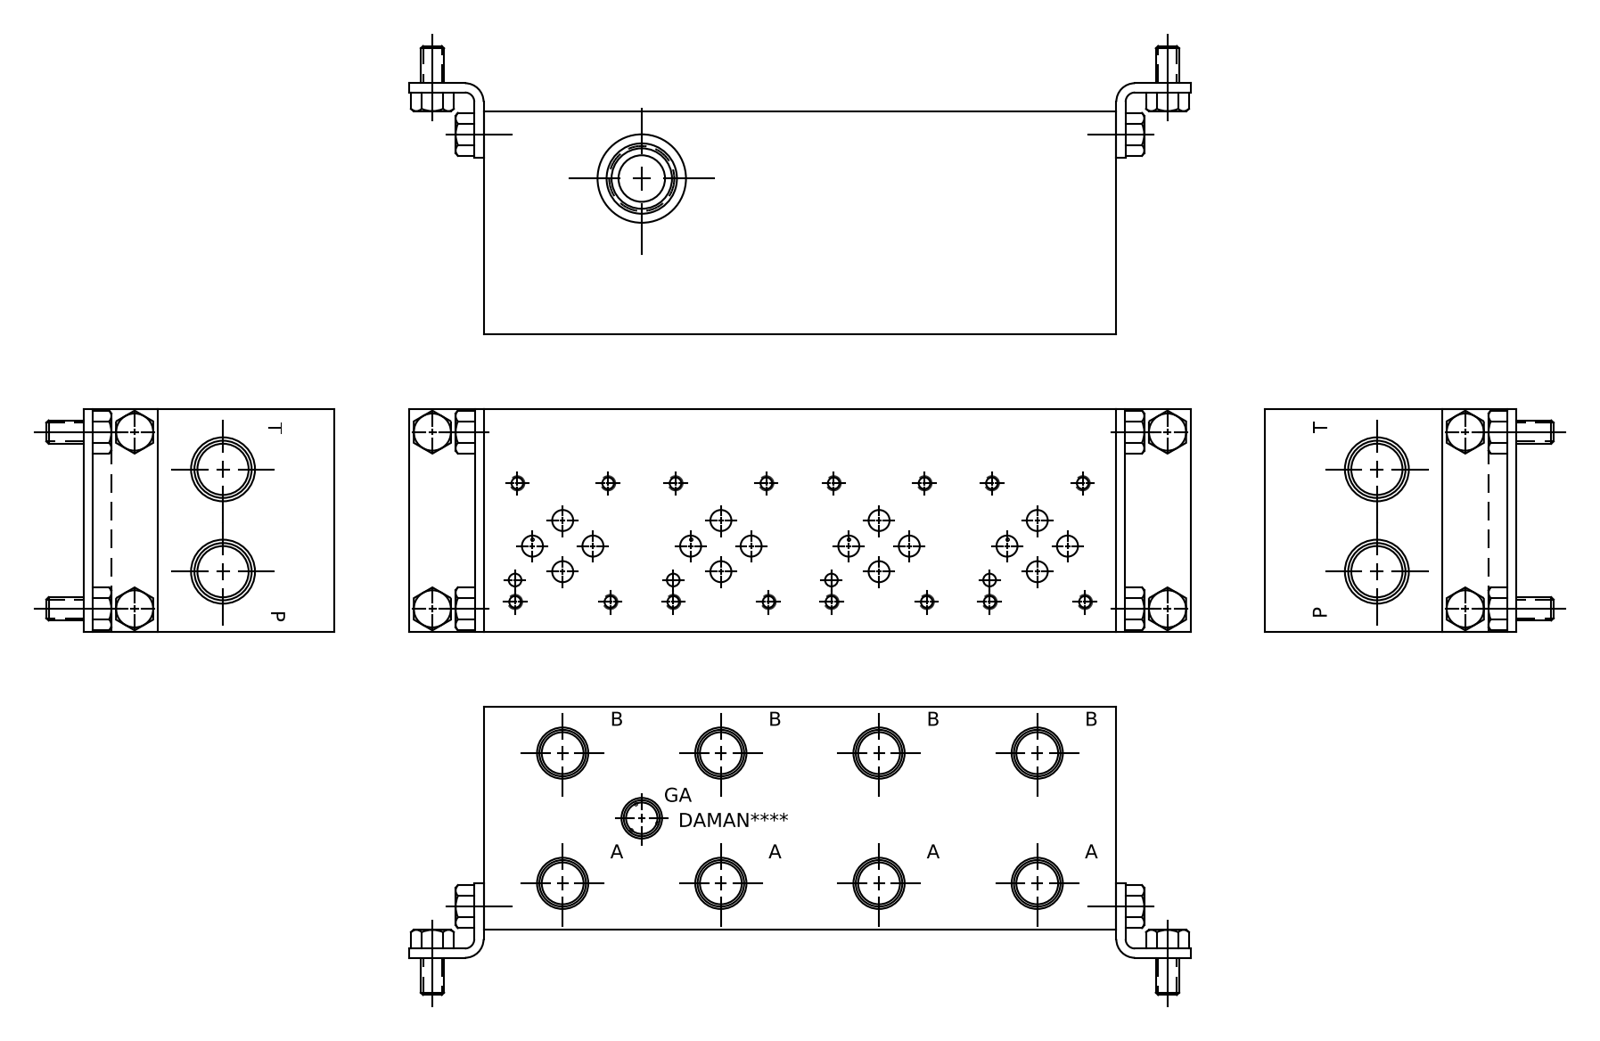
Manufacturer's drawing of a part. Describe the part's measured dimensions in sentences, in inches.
The part is named "Part_AD03P042P~C_3D". Its 3-D file was written by "Autodesk Inventor 2019 (AUTOMOTIVE_DESIGN)". It is 1 solid with 778 faces: 432 planar, 96 cylindrical and 250 other. Overall it measures 8.5 by 3 by 3 inches. Its volume is 71.03 cubic inches and its surface area 157.9 square inches. Round holes: 16 of diameter 0.149, 16 of diameter 0.19, 12 of diameter 0.281, 8 of diameter 0.563, 8 of diameter 0.681, 4 of diameter 0.156, 4 of diameter 0.25, 2 of diameter 0.257, 2 of diameter 0.312, 2 of diameter 0.625, 2 of diameter 0.688, 2 of diameter 0.85. The main face-to-face distances are 3, 8.5, 0.462, 2.538, 0.605, 7.895, 0.039, 2.876, 2.414, 0.124. The hole center spacings are 4.25, 2.125, 2.125, 6.375, 0.785, 0.868, 1.321, 2.026.
